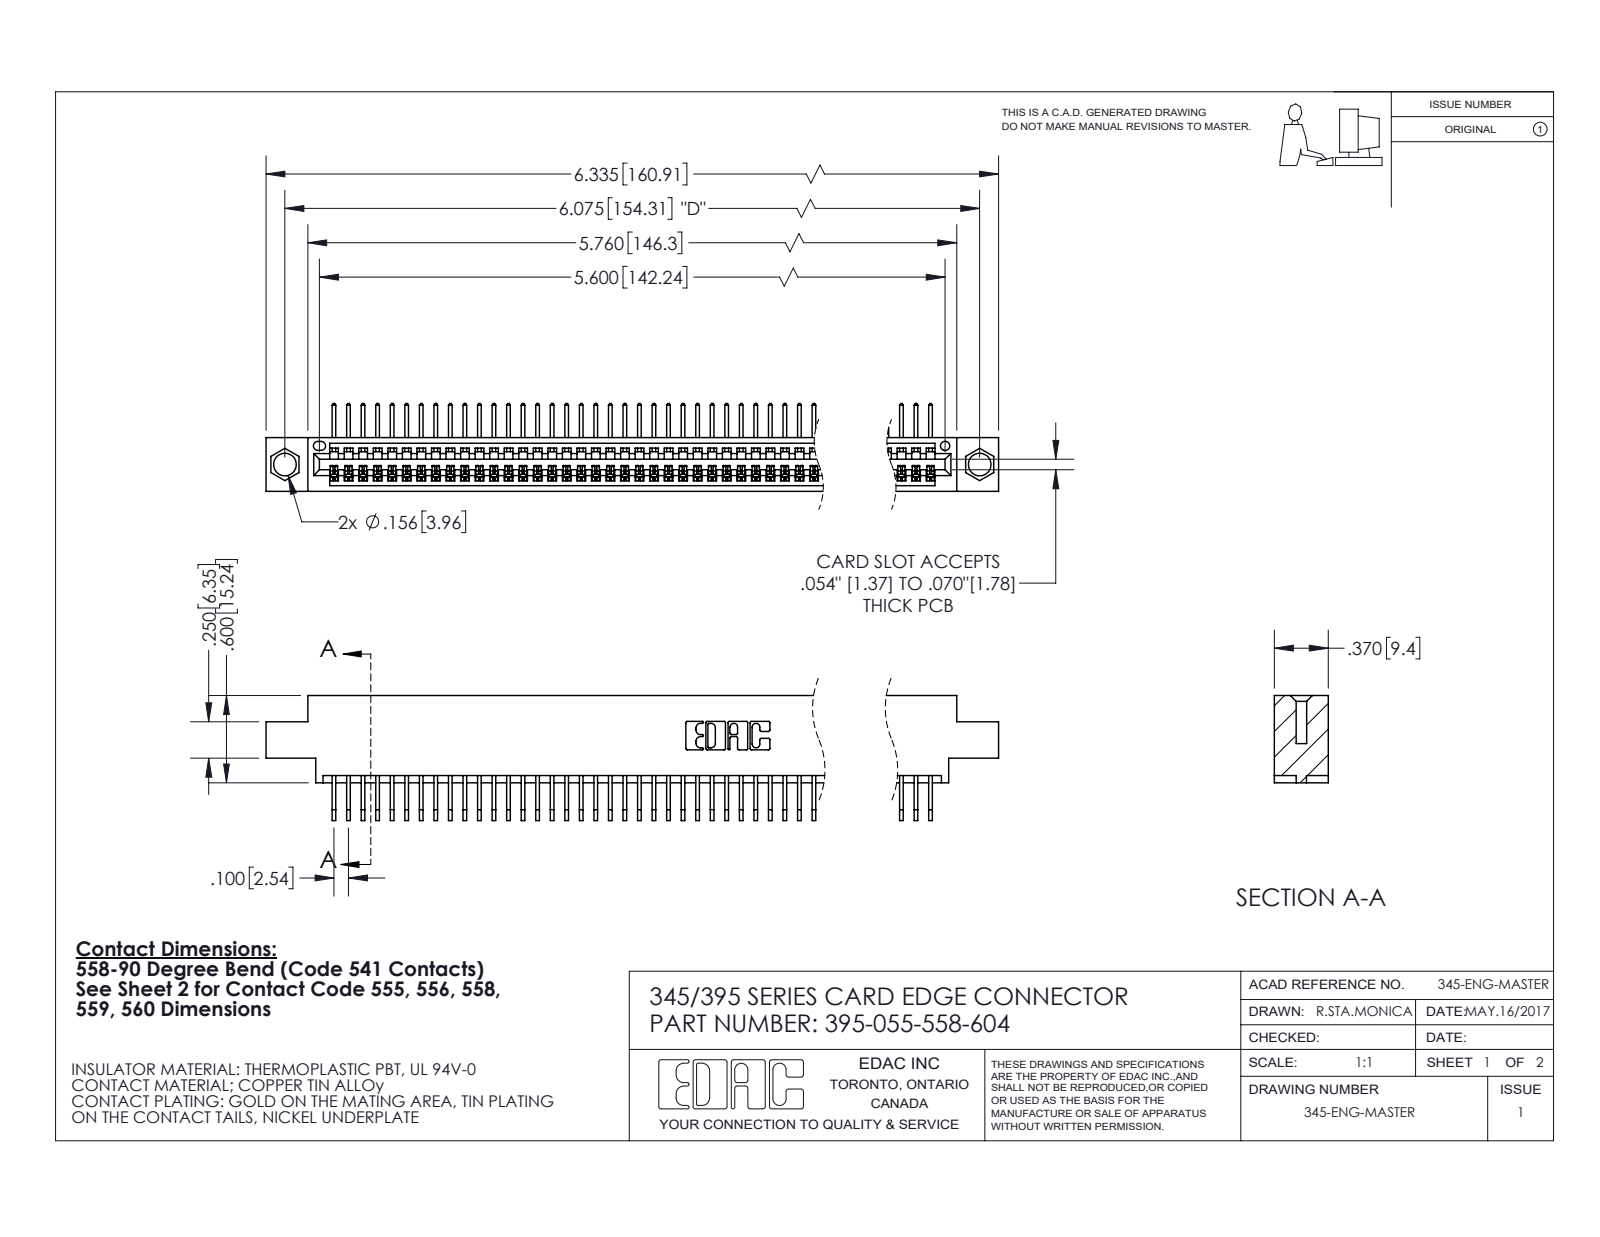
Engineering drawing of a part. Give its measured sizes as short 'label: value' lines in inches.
name: 395-055-558-604; 345 Part_0.170 Offset - 0.156 Dia-TI; 345-292-001_558 Tail - 2
written by: SolidWorks 2020 (CONFIG_CONTROL_DESIGN)
unit: in
bodies: 56 solids, 3444 faces (2408 planar, 1036 cylindrical, 0 other)
size: 6.335 × 0.859 × 0.605
volume: 0.937 in³; area: 33.52 in²
holes: 2× ⌀0.156, 1× ⌀0.064
rounds: 110× R0.006, 22× R0.01, 6× R0.007, 6× R0.031, 3× R0.026, 2× R0.031, 2× R0.04, 1× R0.014
face distances: 0.072, 0.298, 0.37, 0.2, 0.098, 0.272, 0.025, 0.225, 0.175, 0.149
hole spacings: 0.27, 5.839, 6.075
